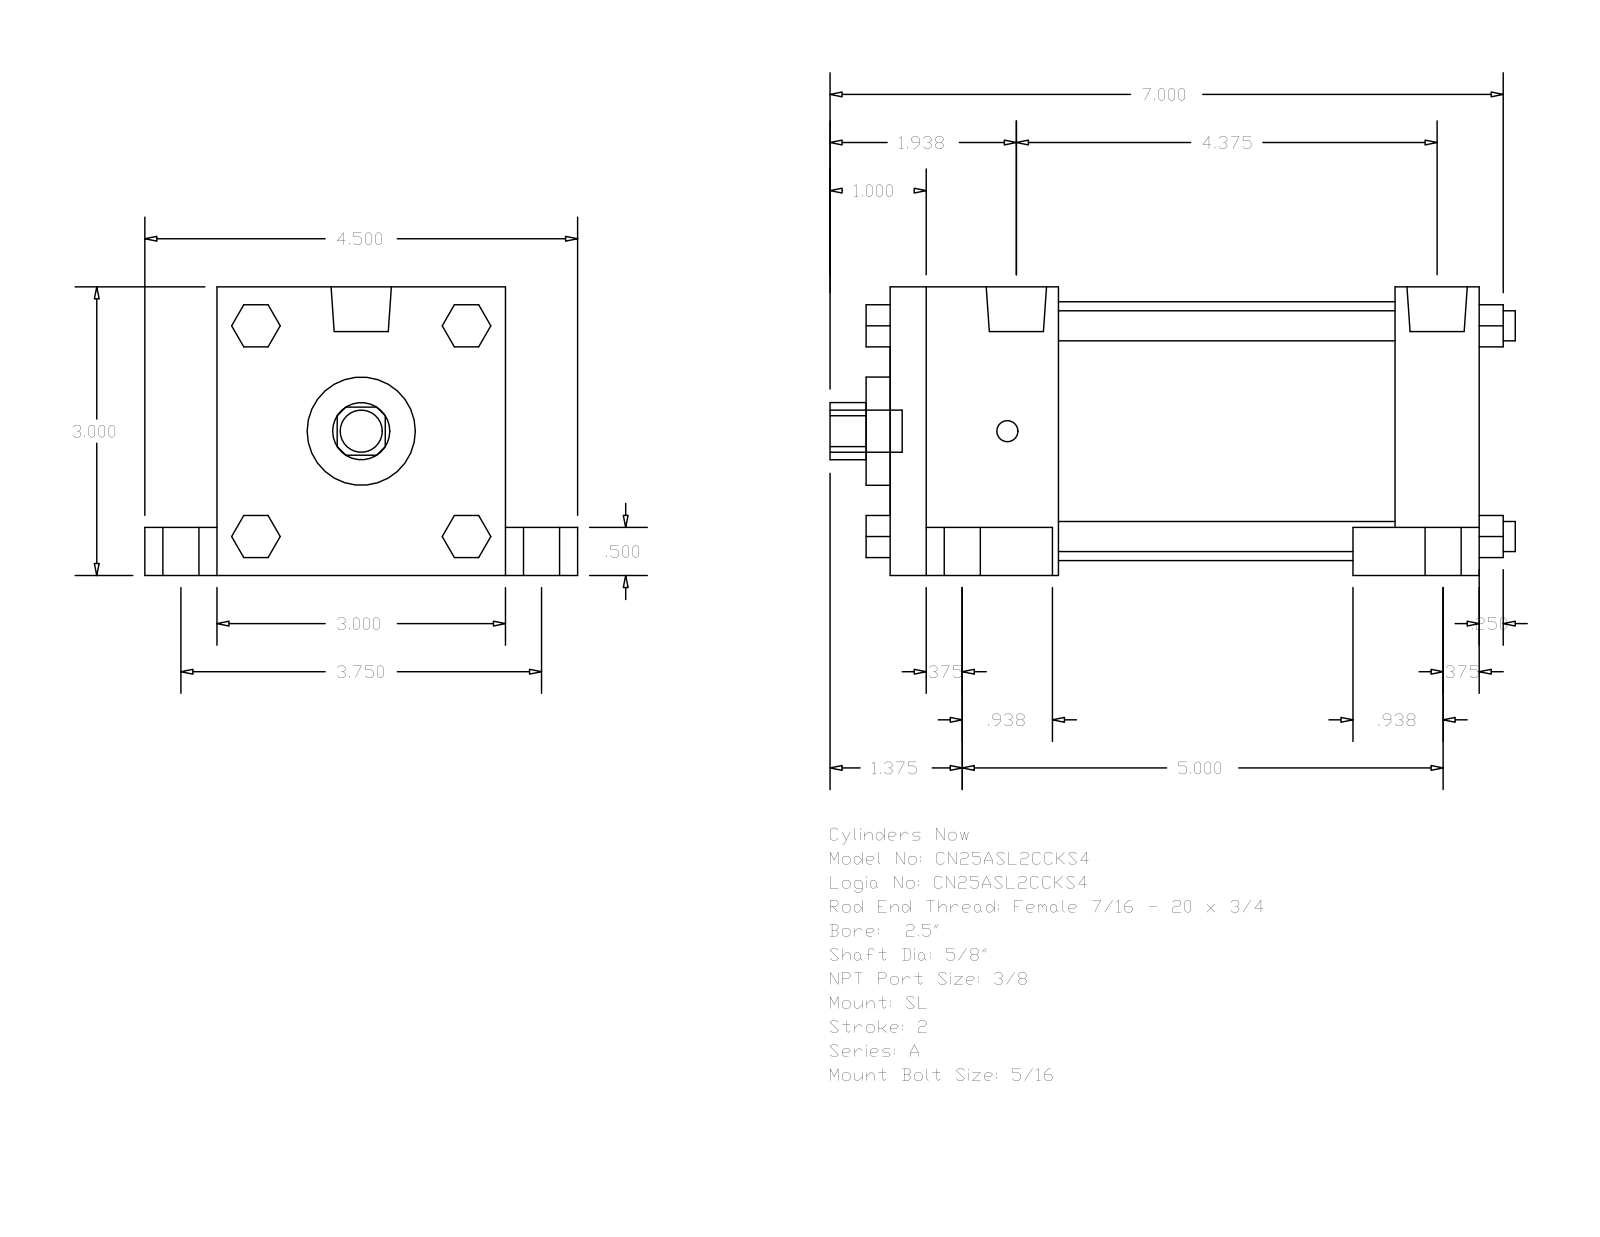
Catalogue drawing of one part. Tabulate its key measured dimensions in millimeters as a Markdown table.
| quantity | value |
| --- | --- |
| part name | A_SL__0250_0.625 |
| STEP written by | GSSL Pune (CONFIG_CONTROL_DESIGN) |
| units | millimeters |
| bodies | 0 solids, 148 faces (112 planar, 36 cylindrical, 0 other) |
| overall size | 180.97 × 114.3 × 76.2 |
| round holes (diameter × count) | 15.88 × 1, 28.57 × 1, 68.33 × 1 |
| round bosses / shafts (diameter × count) | 15.88 × 4, 9.53 × 4, 7.94 × 4, 5.56 × 4, 15.93 × 2, 11.11 × 1 |
| partial cylindrical surfaces (radius × count) | 7.54 × 1 |
| main face-to-face distances | 76.2, 155.57, 44.45, 111.12, 133.34, 88.89, 22.23, 12.7, 63.5, 19.05 |
